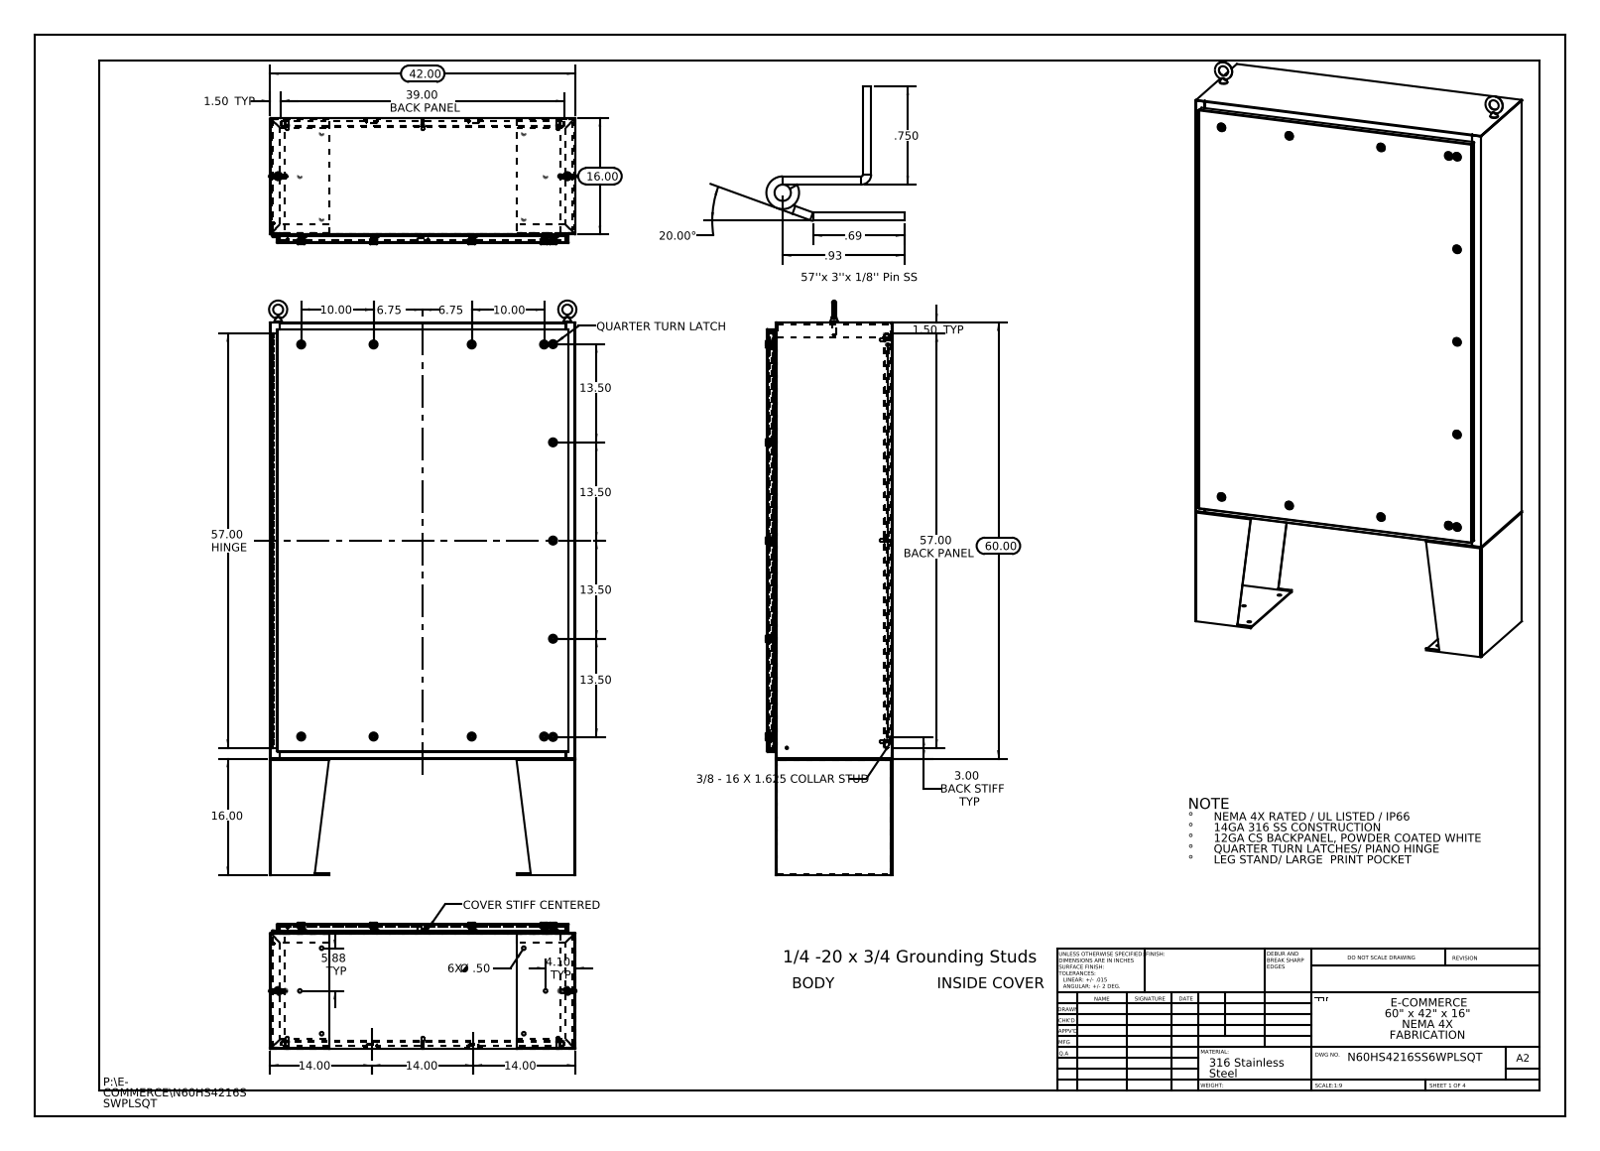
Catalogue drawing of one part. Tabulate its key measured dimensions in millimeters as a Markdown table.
| quantity | value |
| --- | --- |
| part name | N60HS4216SSWPLSQT Backpanel; HW-EYE-NH-20425_3014T52; N60HS4216SSWPLSQT Enclosure Stiffener; N60HS4216SSWPLSQT SD-LSK - Base (+8 more) |
| STEP written by | SolidWorks 2013 (CONFIG_CONTROL_DESIGN) |
| units | millimeters |
| bodies | 36 solids, 2379 faces (1197 planar, 986 cylindrical, 196 other) |
| overall size | 2006.6 × 1073.7 × 436.9 |
| volume | 18 070 000 mm³ |
| surface area | 17 170 000 mm² |
| round holes (diameter × count) | 12.7 × 14, 6.4 × 8, 19.1 × 4, 3.2 × 1, 3.2 × 1 |
| round bosses / shafts (diameter × count) | 15.9 × 10, 9.5 × 8, 8.4 × 8, 4 × 8, 3.6 × 8, 8 × 2, 6 × 2, 6.4 × 1 |
| partial cylindrical surfaces (radius × count) | 0.3 × 36, 2.2 × 30, 11.2 × 13, 1 × 8, 3.6 × 8, 0.5 × 6, 3 × 4, 3.2 × 4 |
| main face-to-face distances | 1.9, 435, 2.6, 433.1, 27.3, 436.9, 25.4, 409.6, 407.7, 29.9 |
| hole center spacings | 56.5, 213.2, 701.7, 796.2, 846.3, 870.9, 1178, 1480.9 |
